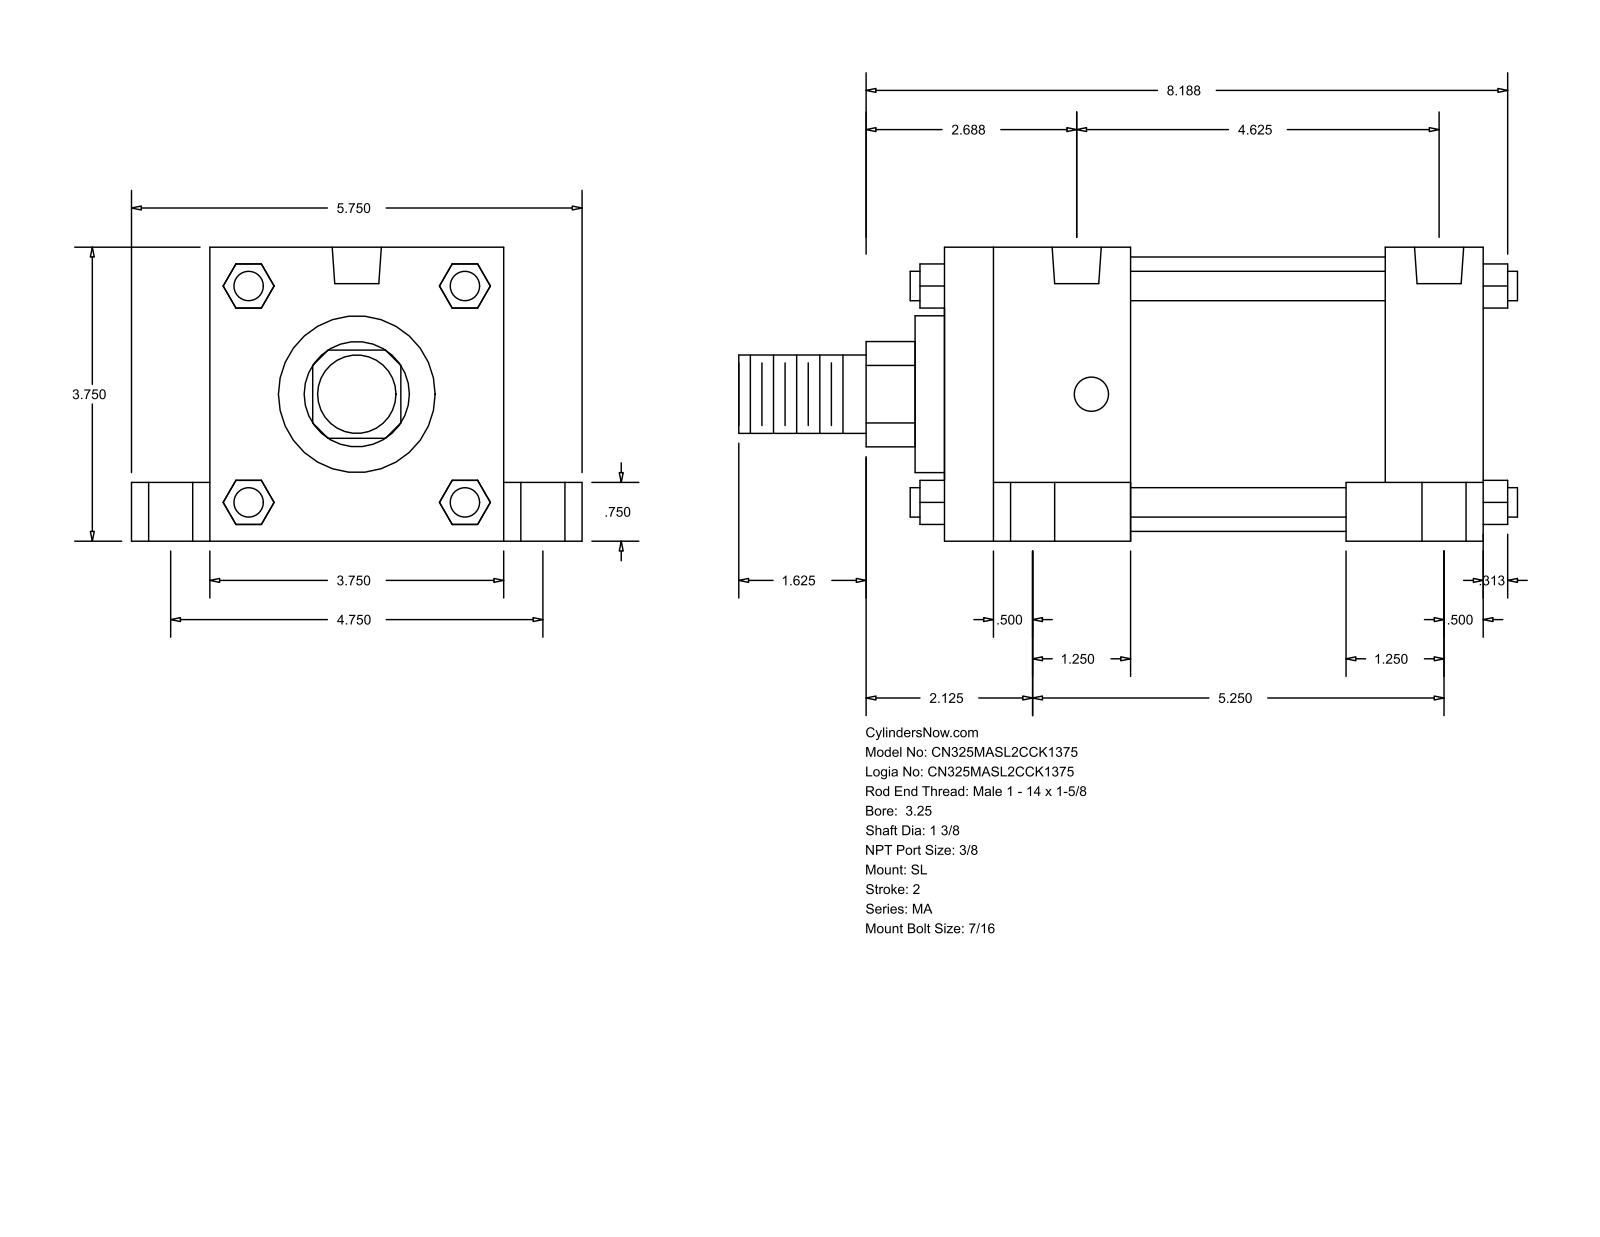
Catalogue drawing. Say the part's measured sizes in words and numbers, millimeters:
The part is named "MA_SL__0325_1.375". Its 3-D file was written by "GSSL Pune (CONFIG_CONTROL_DESIGN)". It is 0 solids with 148 faces: 112 planar, 36 cylindrical and 0 other. Overall it measures 252.41 by 146.05 by 95.25 millimeters. Round holes: 4 of diameter 11.11, 4 of diameter 14.29, 4 of diameter 20.64, 2 of diameter 15.93. Round bosses or shafts: 4 of diameter 9.53, 1 of diameter 88.9, 1 of diameter 50.8, 1 of diameter 34.92, 1 of diameter 25.4. Partial cylindrical surfaces (rounded edges, fillets, slot ends): 1 of radius 17.06. The main face-to-face distances are 95.24, 174.63, 25.41, 120.65, 142.88, 31.75, 60.32, 82.56, 114.31, 19.05. The hole center spacings are 4.77, 60.35, 60.66, 62, 63.27, 107.94, 112.71, 120.66.
